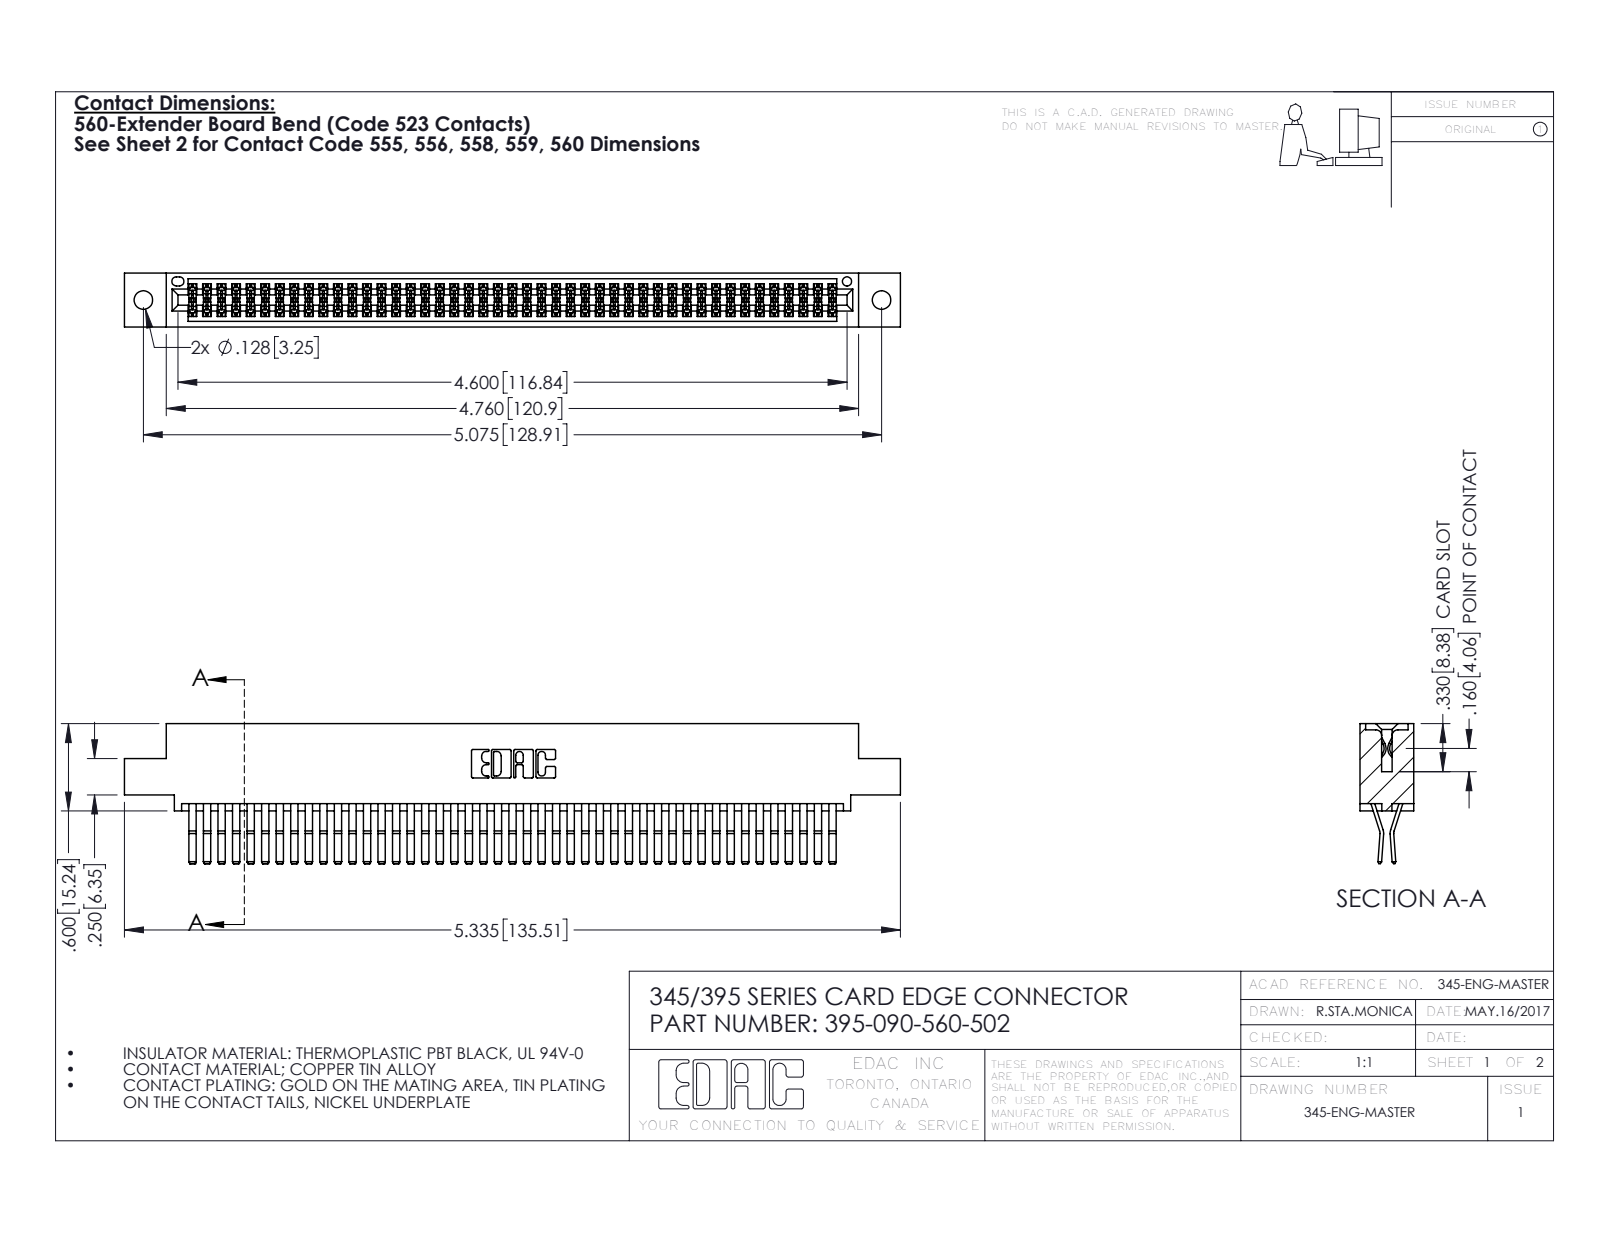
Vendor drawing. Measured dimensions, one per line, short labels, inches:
name: 395-090-560-502; 345-292-001_560 Tail; 345 Part_0.110 Offset - 0.128 Dia
written by: SolidWorks 2016 (CONFIG_CONTROL_DESIGN)
unit: in
bodies: 91 solids, 4810 faces (3054 planar, 1756 cylindrical, 0 other)
size: 5.335 × 0.962 × 0.37
volume: 0.834 in³; area: 33.49 in²
holes: 2× ⌀0.128, 1× ⌀0.064
rounds: 135× R0.006, 22× R0.01, 6× R0.007, 6× R0.031, 3× R0.026, 2× R0.01, 2× R0.014, 2× R0.019
face distances: 0.025, 0.298, 0.072, 0.37, 0.2, 0.098, 0.272, 0.225, 0.175, 0.149
hole spacings: 0.27, 4.839, 5.075
